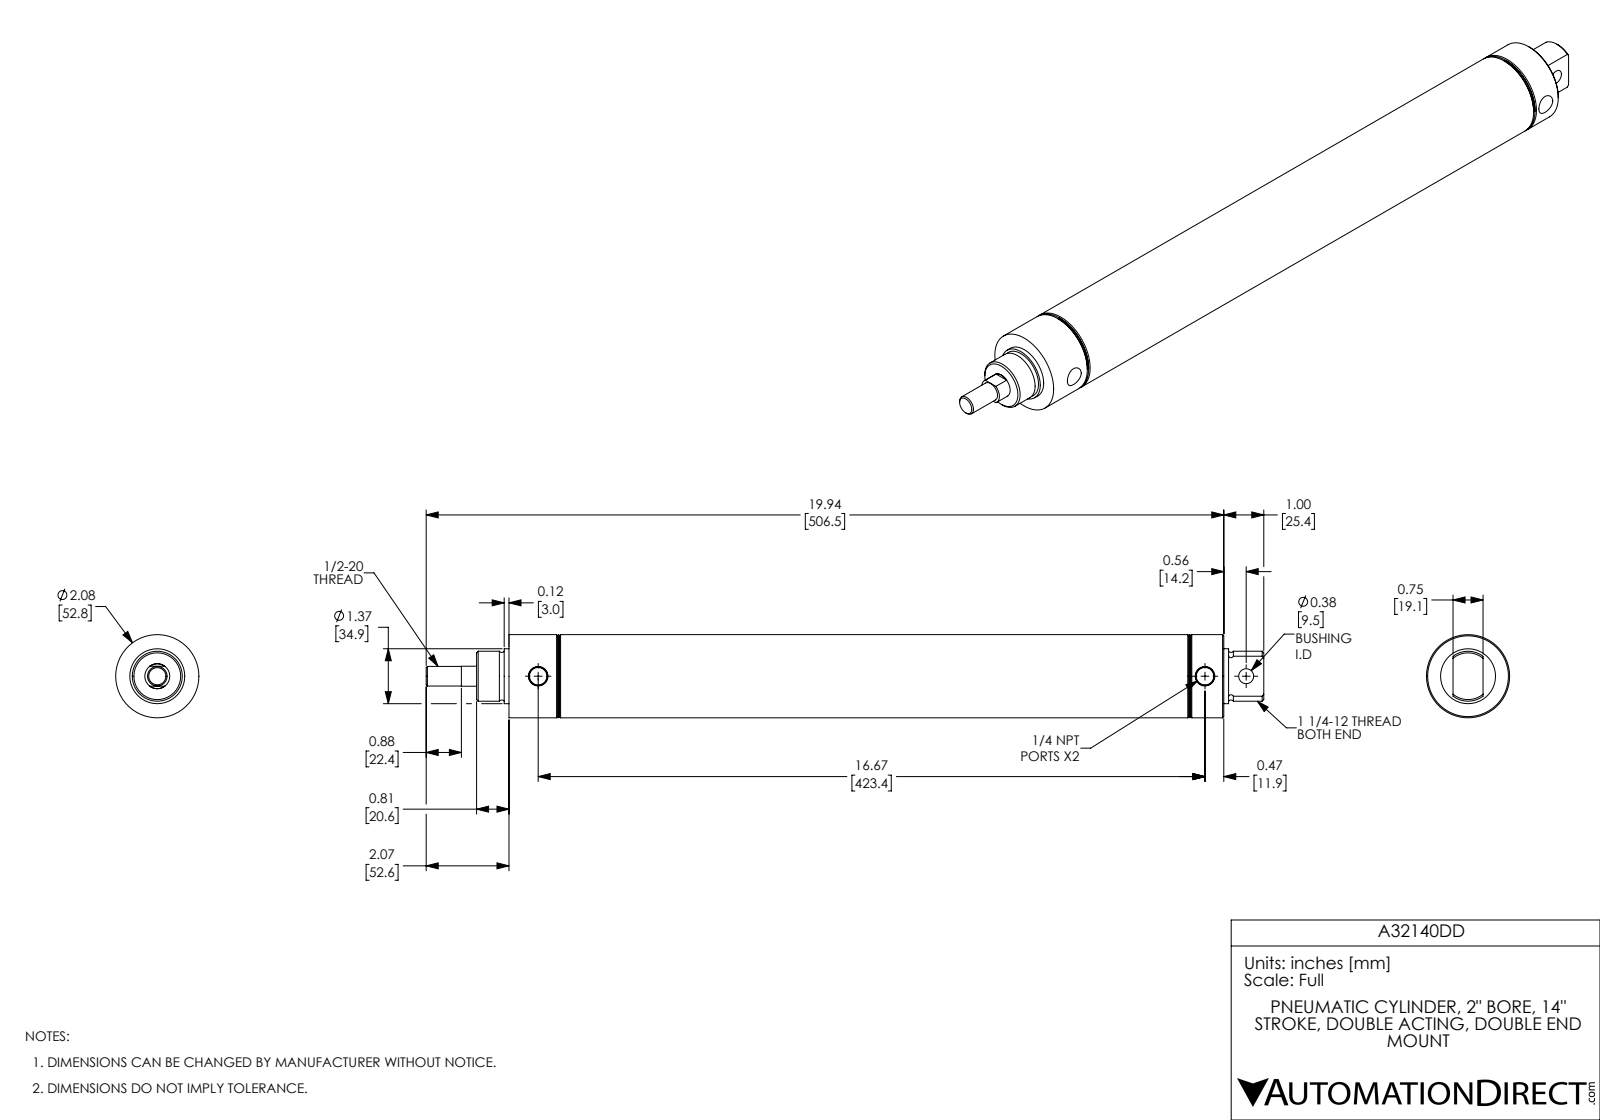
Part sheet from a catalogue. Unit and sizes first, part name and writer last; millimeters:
Units: millimetres
Overall size (bounding box): 531.9 × 52.8 × 52.8
Round holes (diameter × count): ⌀11.1 ×2, ⌀9.5 ×1, ⌀15.9 ×1, ⌀50.8 ×1
Round bosses / shafts (diameter × count): ⌀52.8 ×1, ⌀34.9 ×1, ⌀31.8 ×1, ⌀12.5 ×1
Main face-to-face distances: 12.7, 368.3, 355.6, 411.1, 398.4, 42.8, 42.8, 55.5, 411.1, 453.9
Hole centre spacings: 26.2, 423.4, 449.6
Volume: 374 800 mm³ · Surface area: 180 100 mm²
Bodies: 2 solids, 88 faces (20 planar, 30 cylindrical, 38 other)
Part name (STEP PRODUCT): A32140DD-MainBody; A32140DD; A32140DD-Rod
STEP written by: SolidWorks 2017 (AUTOMOTIVE_DESIGN)
